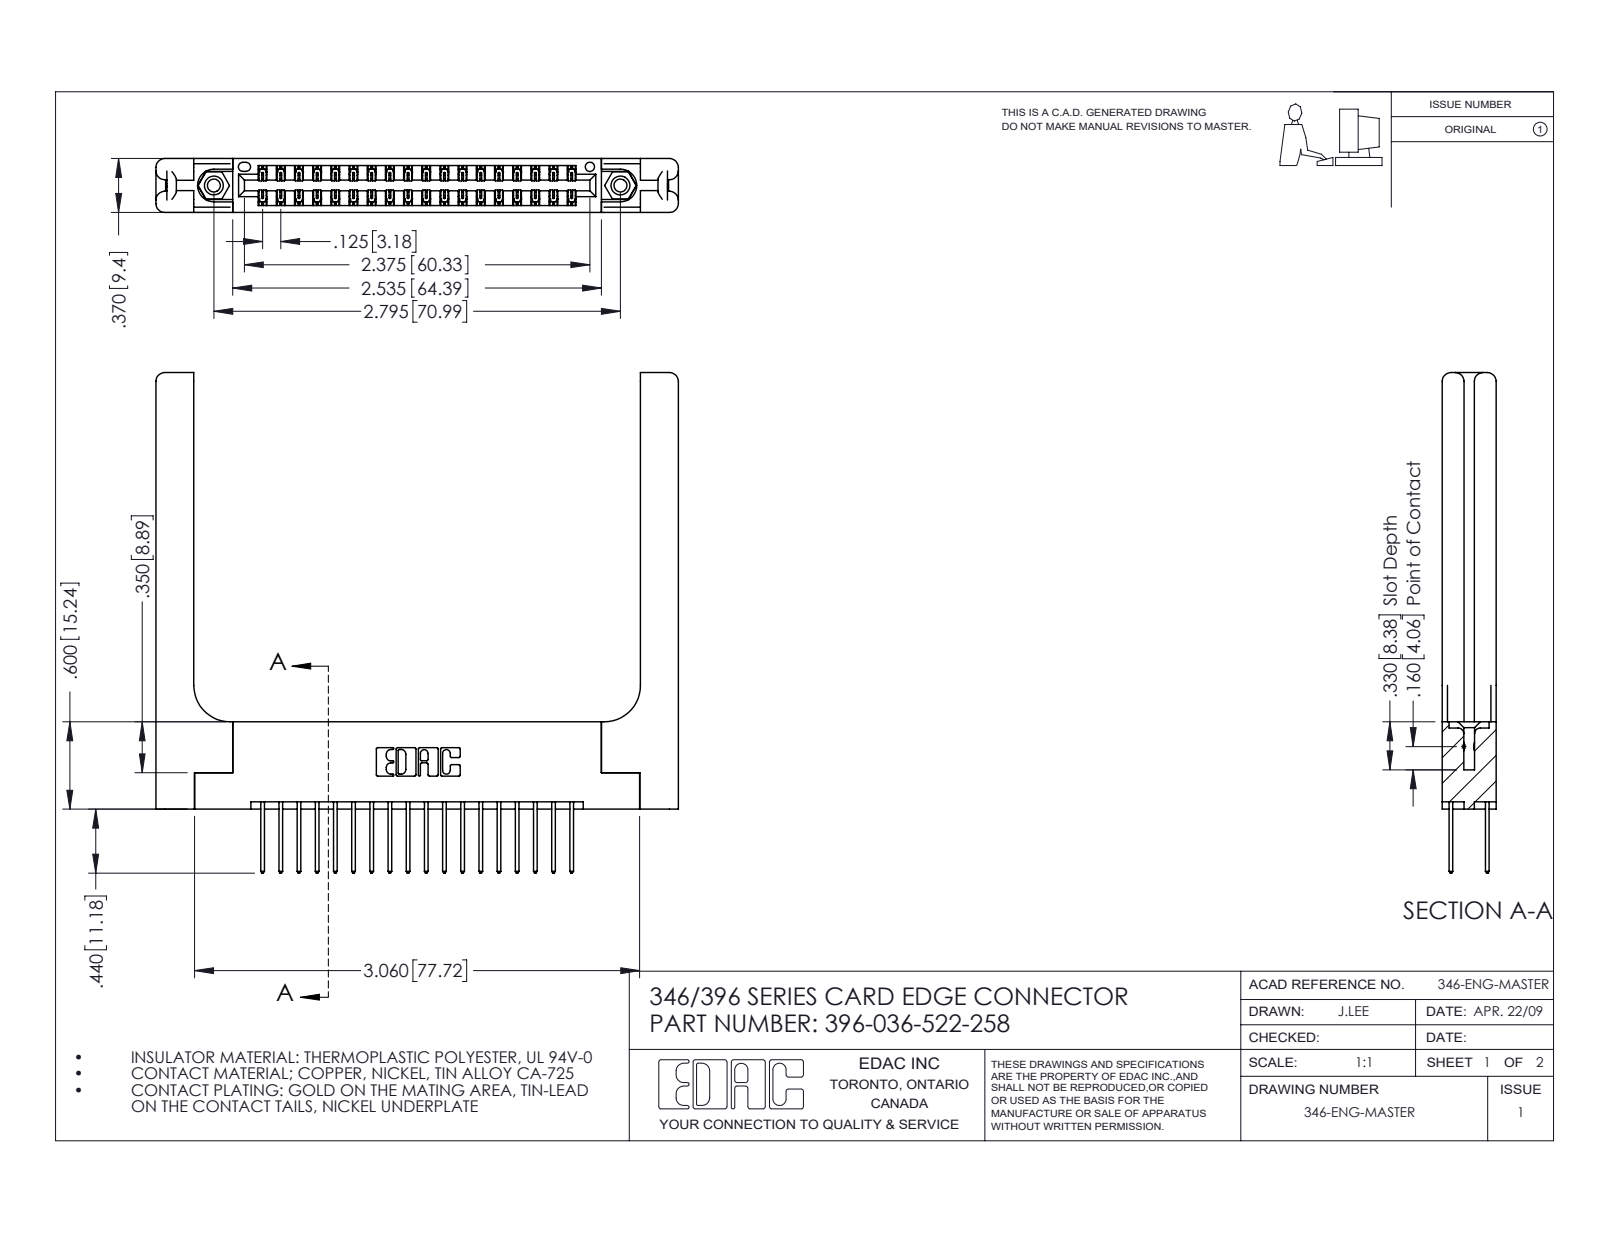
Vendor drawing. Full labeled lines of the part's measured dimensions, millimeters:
Part name (STEP PRODUCT): 345-250-001_345-250-001-102; 346 Part_Flush Mounting Lugs - 0.156 Dia-TH; 346-220-058_345-220-058; 345-292-001_345-293-122 (+1 more)
STEP written by: SolidWorks 2016 (CONFIG_CONTROL_DESIGN)
Units: millimetres
Bodies: 41 solids, 2250 faces (1484 planar, 706 cylindrical, 60 other)
Overall size (bounding box): 91.2 × 87.4 × 9.4
Volume: 16 300 mm³ · Surface area: 17 120 mm²
Round holes (diameter × count): ⌀2.3 ×2, ⌀3.2 ×2, ⌀4 ×2, ⌀1.6 ×1
Round bosses / shafts (diameter × count): ⌀3.9 ×2
Partial cylindrical surfaces — rounded edges, fillets, slot ends (radius × count): R0.2 ×54, R0.3 ×36, R0.3 ×22, R1.5 ×16, R0.2 ×6, R0.8 ×6, R0.7 ×3, R0.4 ×2
Main face-to-face distances: 9.4, 1.8, 1.2, 8.2, 3.8, 3.8, 6.4, 0.6, 7.6, 2
Hole centre spacings: 6.2, 65.7, 71
